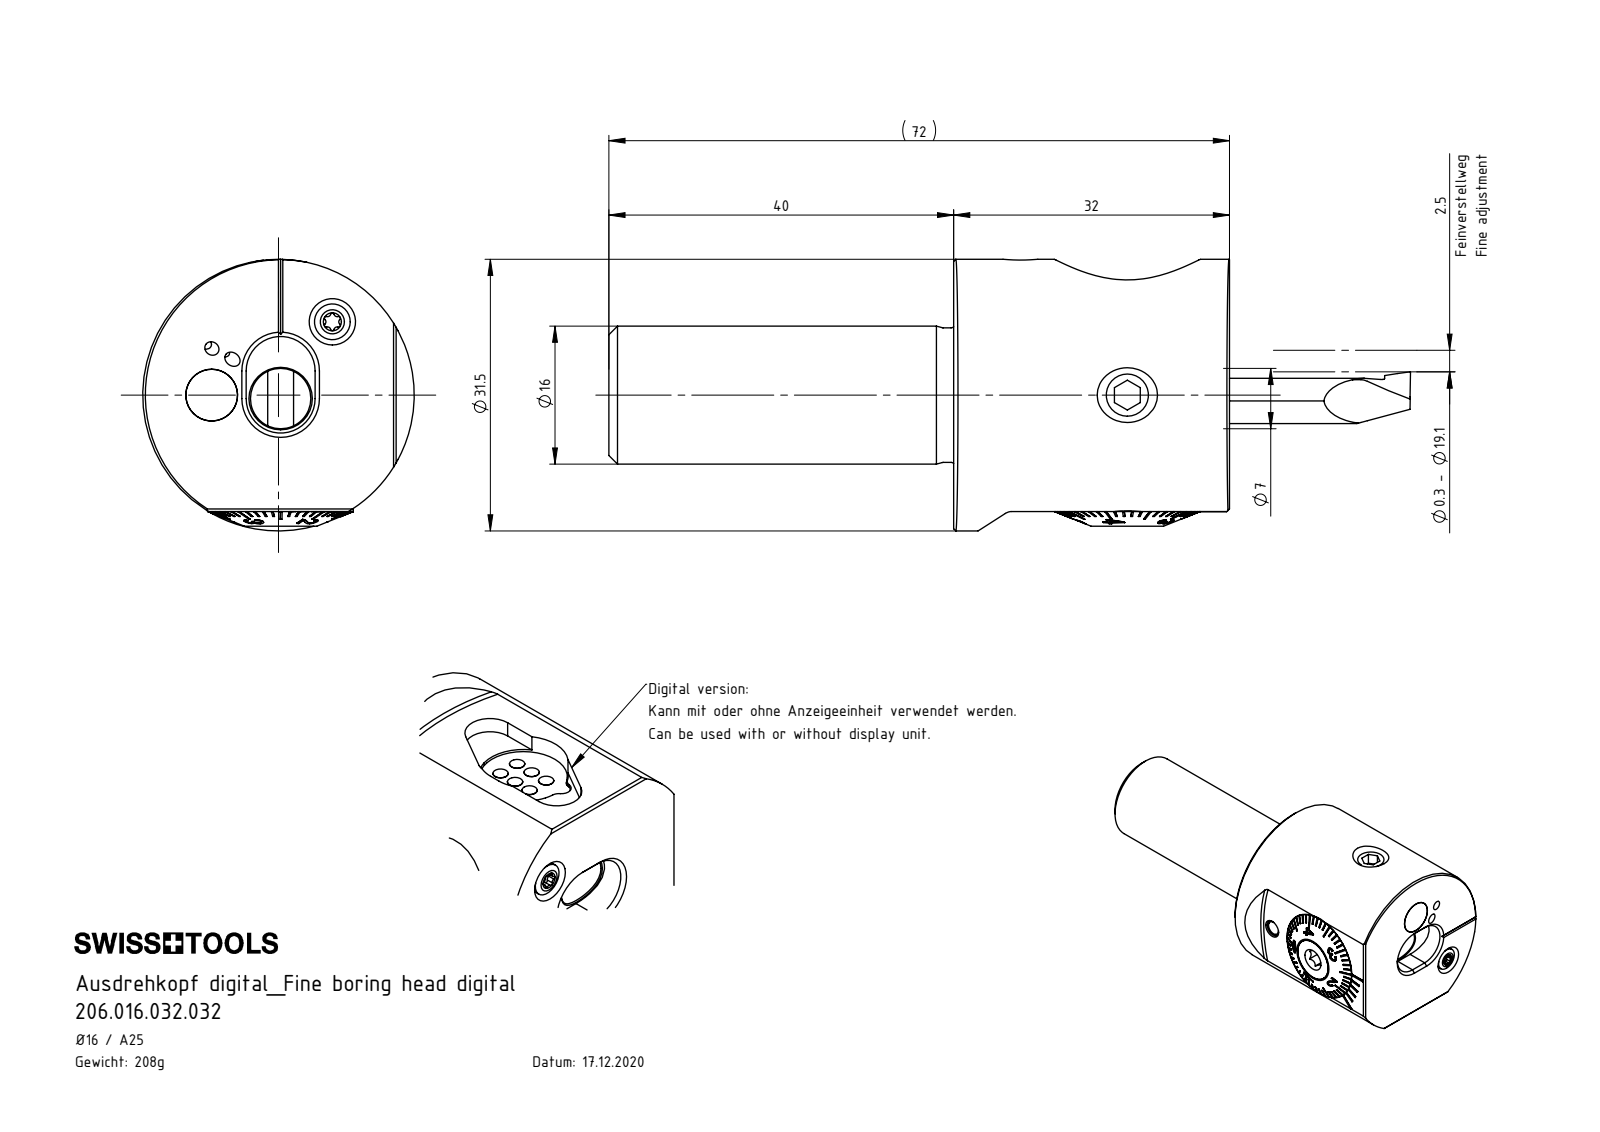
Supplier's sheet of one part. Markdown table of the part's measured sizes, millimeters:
| quantity | value |
| --- | --- |
| part name | Mini_Schaft_7; PEE-DA1.011.026_A; Klebstoff D6; Axx-BG4.003.xxx_A_A32 (+8 more) |
| STEP written by | SolidWorks 2017 (CONFIG_CONTROL_DESIGN) |
| units | millimeters |
| bodies | 18 solids, 822 faces (360 planar, 180 cylindrical, 282 other) |
| overall size | 98 × 32 × 32 |
| volume | 28 567 mm³ |
| surface area | 17 901 mm² |
| round holes (diameter × count) | 5 × 7, 3.3 × 2, 0.7 × 1, 1 × 1, 2 × 1, 2.5 × 1, 2.9 × 1, 3 × 1, 6 × 1, 7 × 1, 7.75 × 1, 8.4 × 1 |
| round bosses / shafts (diameter × count) | 1.9 × 6, 6 × 3, 32 × 1, 17 × 1, 16.98 × 1, 16.85 × 1, 16 × 1, 15.6 × 1 |
| partial cylindrical surfaces (radius × count) | 0.21 × 6, 0.36 × 5, 0.2 × 4, 2.2 × 4, 1.1 × 3, 1.2 × 3, 3.1 × 2, 4 × 2 |
| main face-to-face distances | 32, 4.5, 1.5, 0.8, 0.4, 4.1, 2.6, 6.8, 2.3, 4.9 |
| hole center spacings | 4.5, 6.96, 13, 2.61, 2.84, 7.9, 8, 9 |
